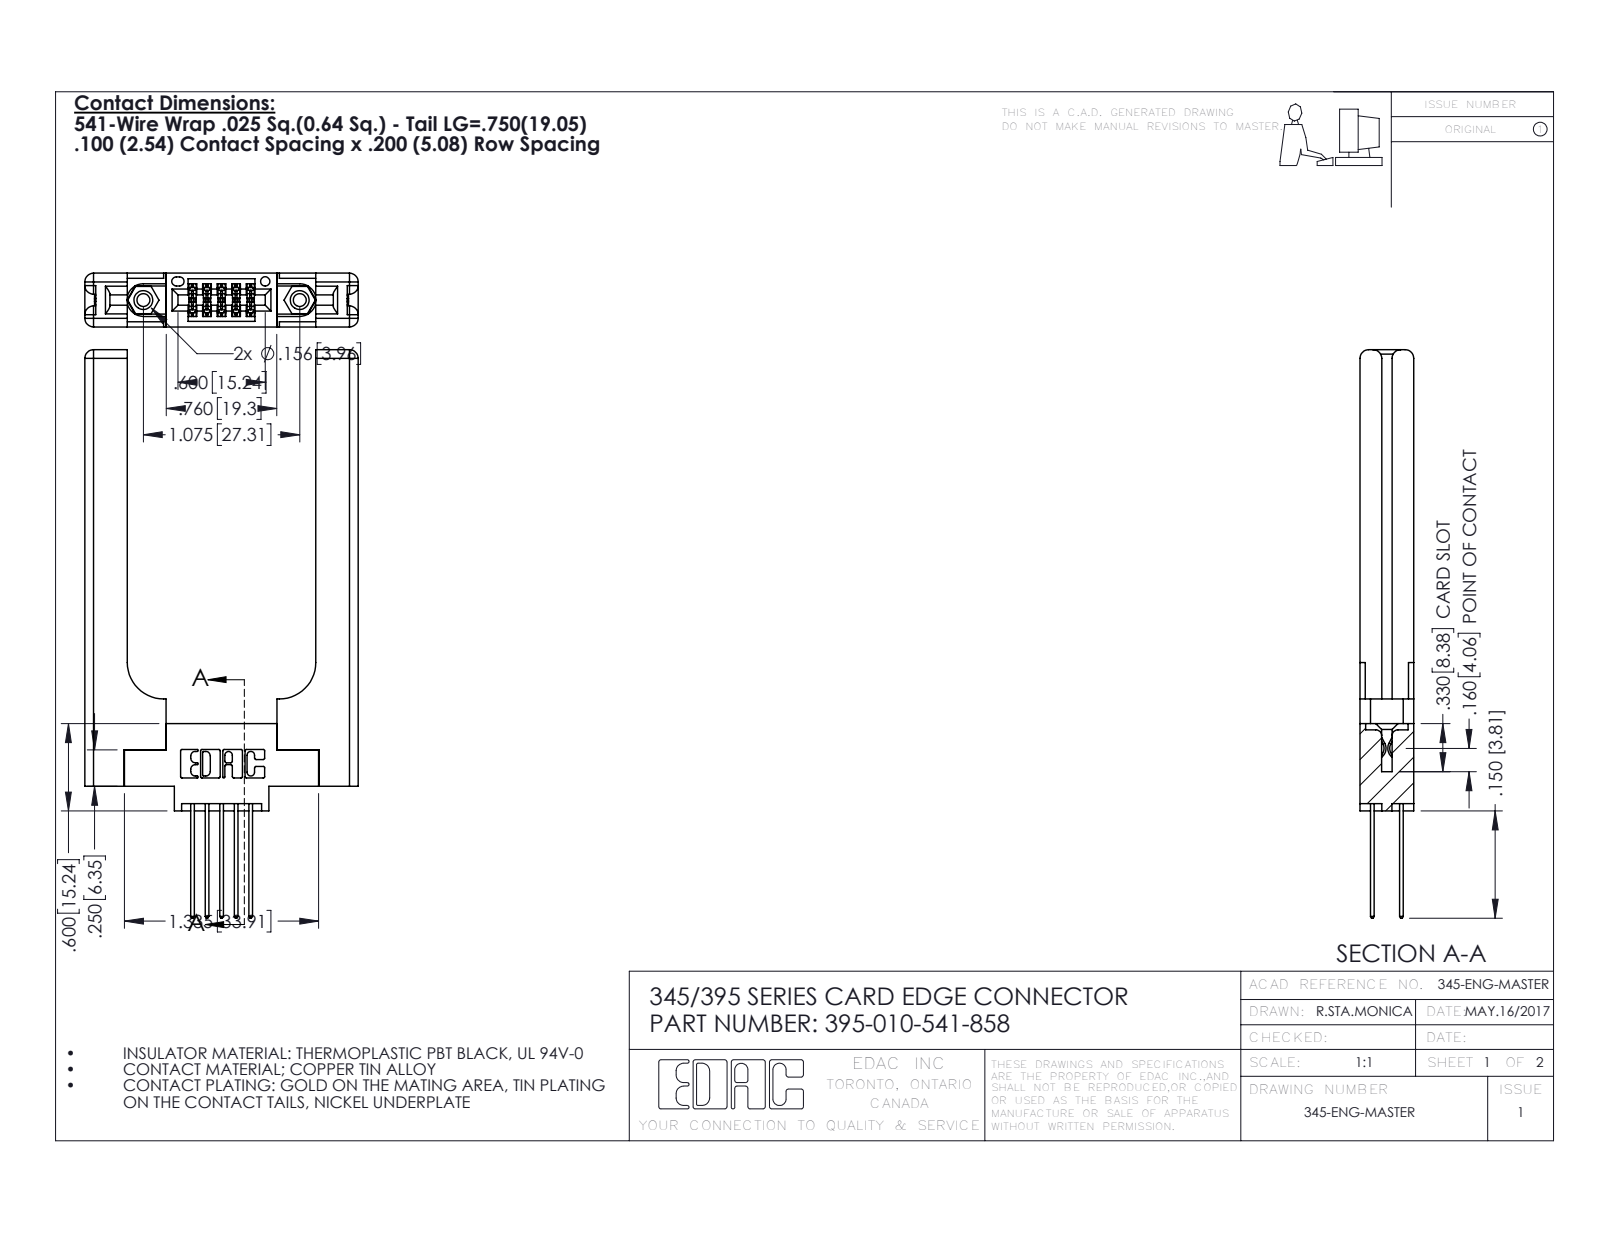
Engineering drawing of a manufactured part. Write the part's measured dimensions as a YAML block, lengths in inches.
part_name: "395-010-541-858; 345-250-001_345-250-001-102; 345 Part_0.170 Offset - 0.156 Dia-TH; 345-292-001_345-293-141 (+1 more)"
step_written_by: "SolidWorks 2016 (CONFIG_CONTROL_DESIGN)"
units: inches
bodies: {solids: 15, faces: 886, planar: 562, cylindrical: 264, other: 60}
overall_size: [3.907, 1.879, 0.37]
volume: 0.776
surface_area: 17.08
round_holes:
  - {diameter: 0.089, count: 2}
  - {diameter: 0.125, count: 2}
  - {diameter: 0.156, count: 2}
  - {diameter: 0.064, count: 1}
round_bosses_or_shafts:
  - {diameter: 0.155, count: 2}
partial_cylinders:
  - {radius: 0.01, count: 22}
  - {radius: 0.06, count: 16}
  - {radius: 0.006, count: 15}
  - {radius: 0.01, count: 10}
  - {radius: 0.007, count: 6}
  - {radius: 0.031, count: 6}
  - {radius: 0.026, count: 3}
  - {radius: 0.014, count: 2}
face_to_face_distances: [0.37, 0.15, 0.22, 0.072, 0.148, 0.077, 0.298, 1.296, 0.071, 0.292]
hole_center_spacings: [0.27, 0.847, 1.075]
